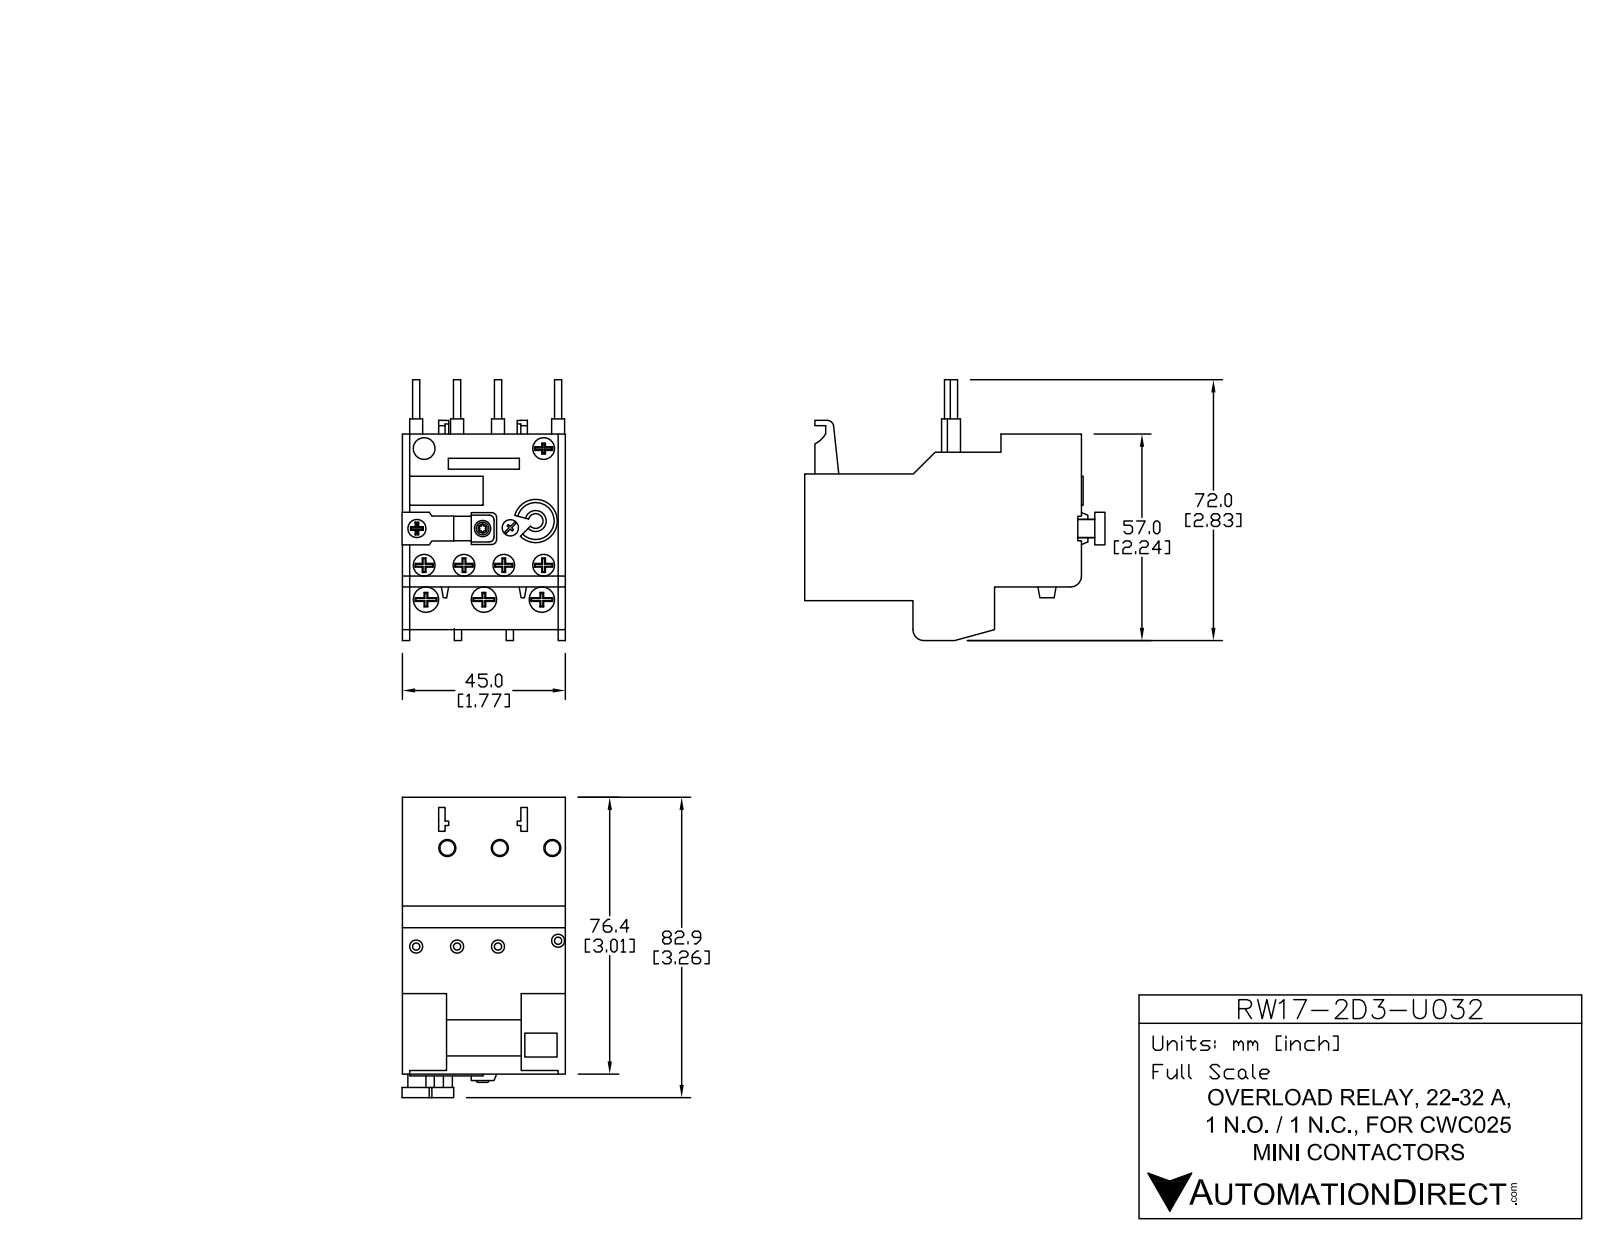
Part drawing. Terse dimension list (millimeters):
name: RW17D-2D3-U032
written by: SolidWorks 2013 (AUTOMOTIVE_DESIGN)
unit: mm
bodies: 17 solids, 748 faces (512 planar, 211 cylindrical, 25 other)
size: 82.65 × 70.5 × 45.55
volume: 127 368 mm³; area: 34 564 mm²
holes: 6× ⌀6, 3× ⌀4, 3× ⌀7, 3× ⌀7.5, 1× ⌀4.5, 1× ⌀4.75, 1× ⌀5.33, 1× ⌀5.5, 1× ⌀10.42
bosses: 7× ⌀5.5, 7× ⌀3, 4× ⌀1.75, 2× ⌀5.6, 2× ⌀3.25, 1× ⌀6.42, 1× ⌀6.15, 1× ⌀4.75
rounds: 20× R0.5, 12× R0.25, 9× R1, 6× R4.52, 4× R5.86, 4× R7.86, 3× R1.5, 2× R1.25
face distances: 45.5, 1.5, 10.85, 11, 76.4, 35, 1.42, 74.98, 74.9, 6
hole spacings: 15, 8.55, 10.75, 30, 10.57, 11.86, 14.25, 21.35
